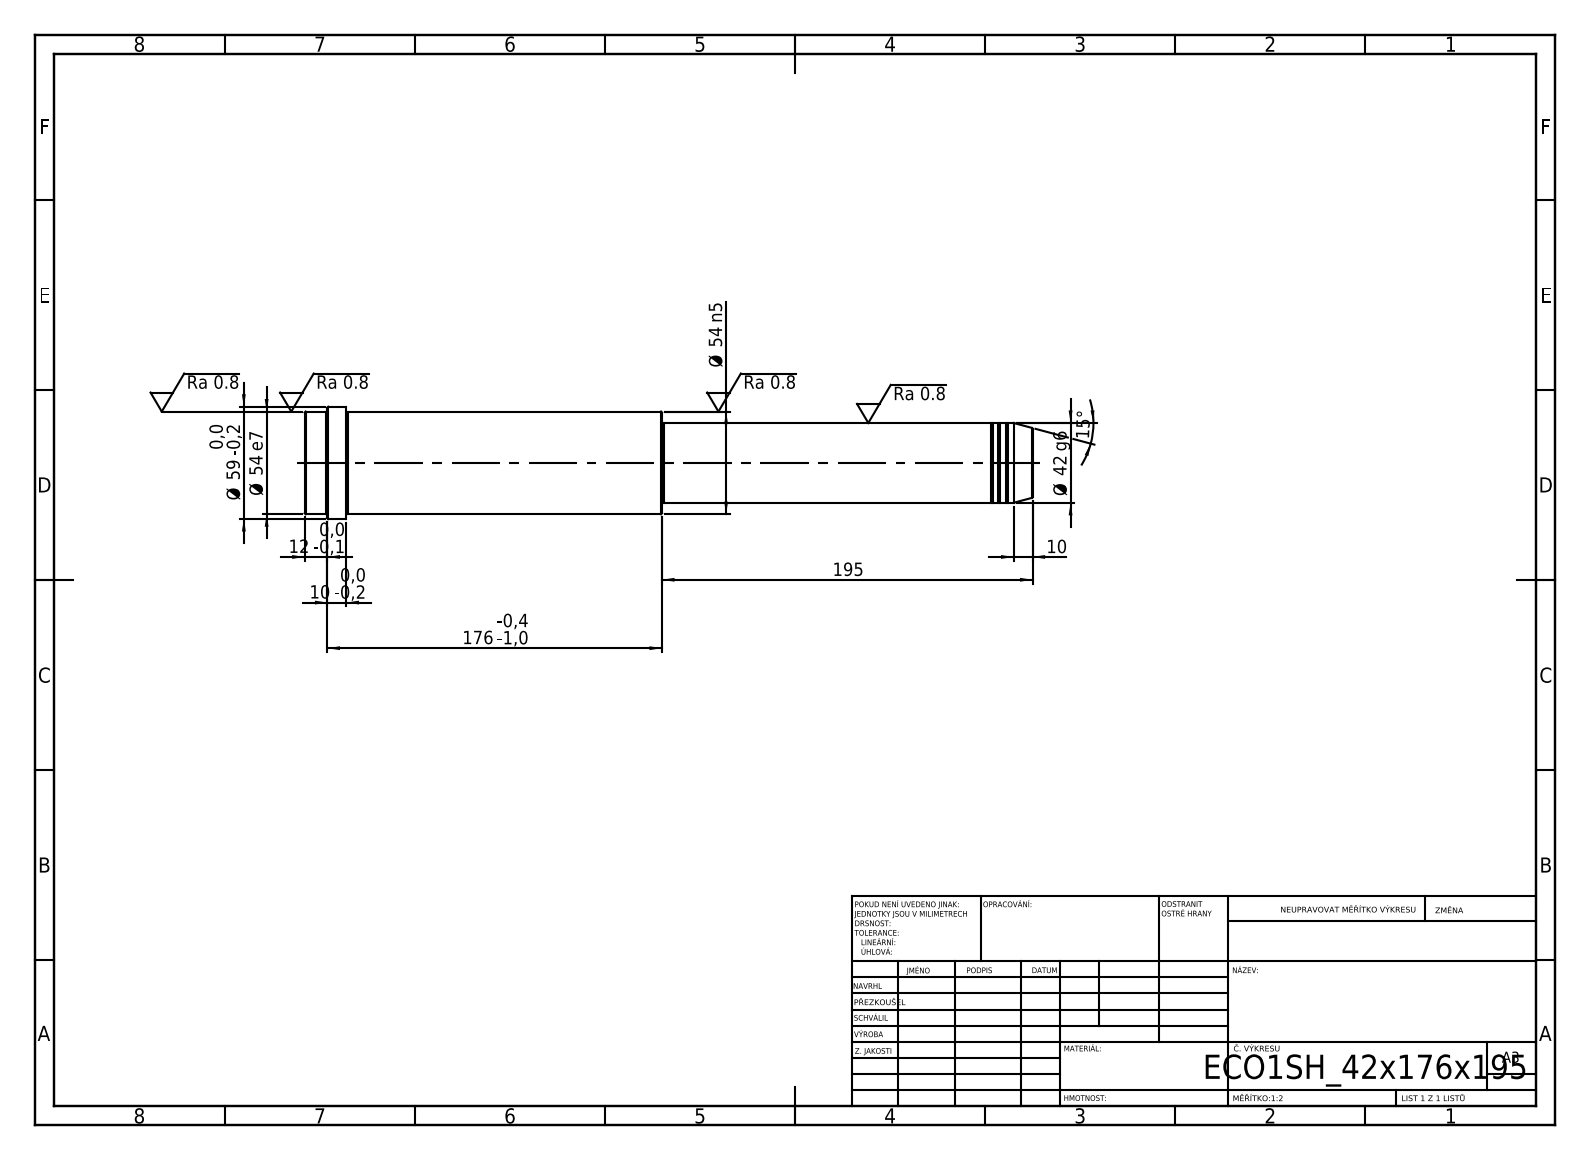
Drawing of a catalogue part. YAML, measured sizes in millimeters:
step_written_by: "SolidWorks 2019 (CONFIG_CONTROL_DESIGN)"
units: millimeters
bodies: {solids: 1, faces: 52, planar: 6, cylindrical: 16, other: 30}
overall_size: [383, 59, 59]
volume: 703048
surface_area: 63240
round_bosses_or_shafts:
  - {diameter: 59, count: 1}
  - {diameter: 54, count: 1}
  - {diameter: 42, count: 1}
  - {diameter: 41, count: 1}
face_to_face_distances: [383, 195, 188, 361, 166, 22, 371, 176, 10, 12]
